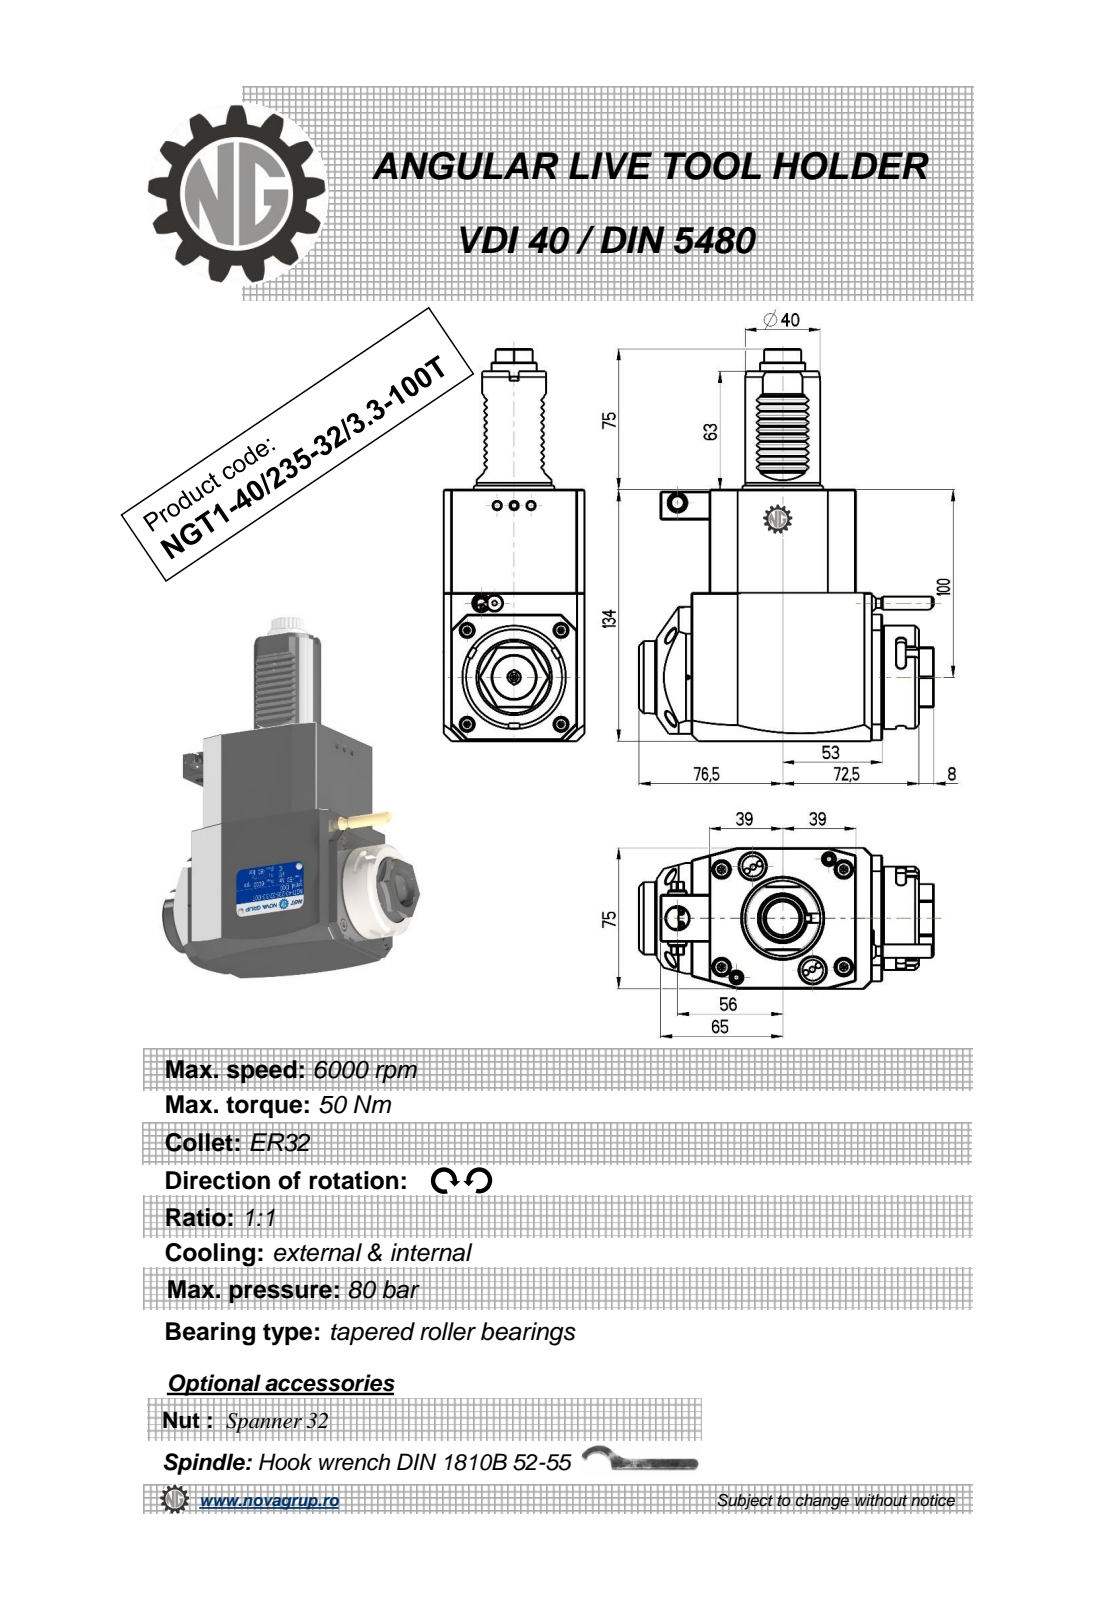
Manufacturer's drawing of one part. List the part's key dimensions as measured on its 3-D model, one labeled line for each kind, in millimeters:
Part name (STEP PRODUCT): NGT1_40_235_32_3_3_100T
STEP written by: PRO/ENGINEER BY PARAMETRIC TECHNOLOGY CORPORATION, 2010280 (CONFIG_CONTROL_DESIGN)
Units: millimetres
Bodies: 1 solid, 540 faces (232 planar, 196 cylindrical, 112 other)
Overall size (bounding box): 209 × 157 × 75
Volume: 1 086 000 mm³ · Surface area: 79 688 mm²
Round holes (diameter × count): ⌀3.3 ×2, ⌀4.5 ×2, ⌀7.5 ×2, ⌀2.5 ×1, ⌀3 ×1, ⌀9.5 ×1, ⌀12 ×1, ⌀23 ×1
Round bosses / shafts (diameter × count): ⌀8 ×2, ⌀55 ×1, ⌀48 ×1, ⌀40 ×1, ⌀38.5 ×1, ⌀24 ×1, ⌀10 ×1, ⌀7 ×1
Partial cylindrical surfaces — rounded edges, fillets, slot ends (radius × count): R2.08 ×48, R0.3 ×20, R2.5 ×6, R180 ×2, R3.85 ×1, R4.25 ×1, R9.08 ×1, R9.92 ×1
Main face-to-face distances: 75, 134, 78, 14, 92, 79, 25, 84.88, 19.5, 111.5
Hole centre spacings: 31.11, 18.07, 43.2, 54.87, 62.23, 72.9, 73.09, 91.5
